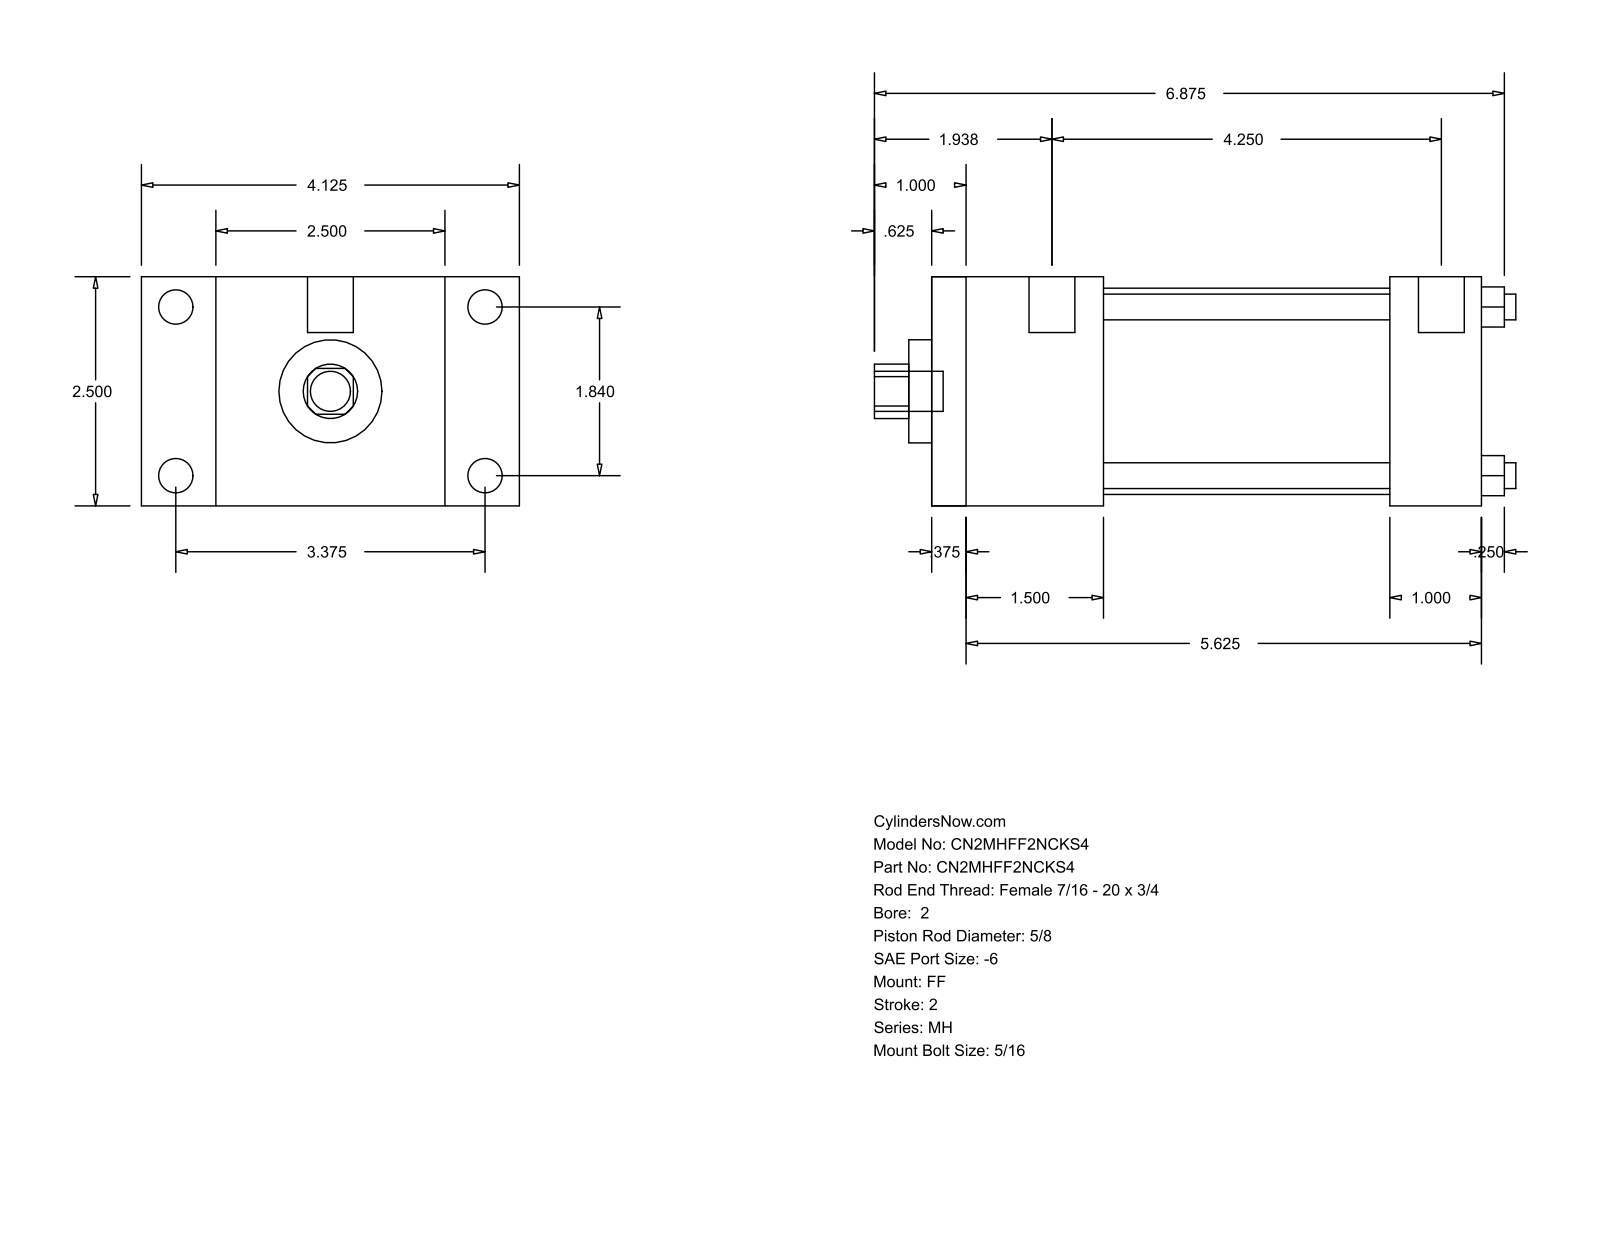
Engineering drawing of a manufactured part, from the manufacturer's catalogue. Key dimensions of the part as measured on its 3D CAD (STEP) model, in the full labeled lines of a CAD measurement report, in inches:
Part name (STEP PRODUCT): MH_FF__0200_0.625
STEP written by: GSSL Pune (CONFIG_CONTROL_DESIGN)
Units: inches
Bodies: 0 solids, 92 faces (64 planar, 28 cylindrical, 0 other)
Overall size (bounding box): 7 × 4.125 × 2.5
Round holes (diameter × count): ⌀0.281 ×4, ⌀0.625 ×1, ⌀1.125 ×1, ⌀2.25 ×1
Round bosses / shafts (diameter × count): ⌀0.375 ×4, ⌀0.219 ×4, ⌀0.5 ×2, ⌀0.437 ×1
Partial cylindrical surfaces — rounded edges, fillets, slot ends (radius × count): R0.297 ×1
Main face-to-face distances: 2.5, 6, 0.375, 5.625, 4.125, 1, 1.5, 1.875, 5, 4.625
Hole centre spacings: 1.301, 1.84, 2.602
